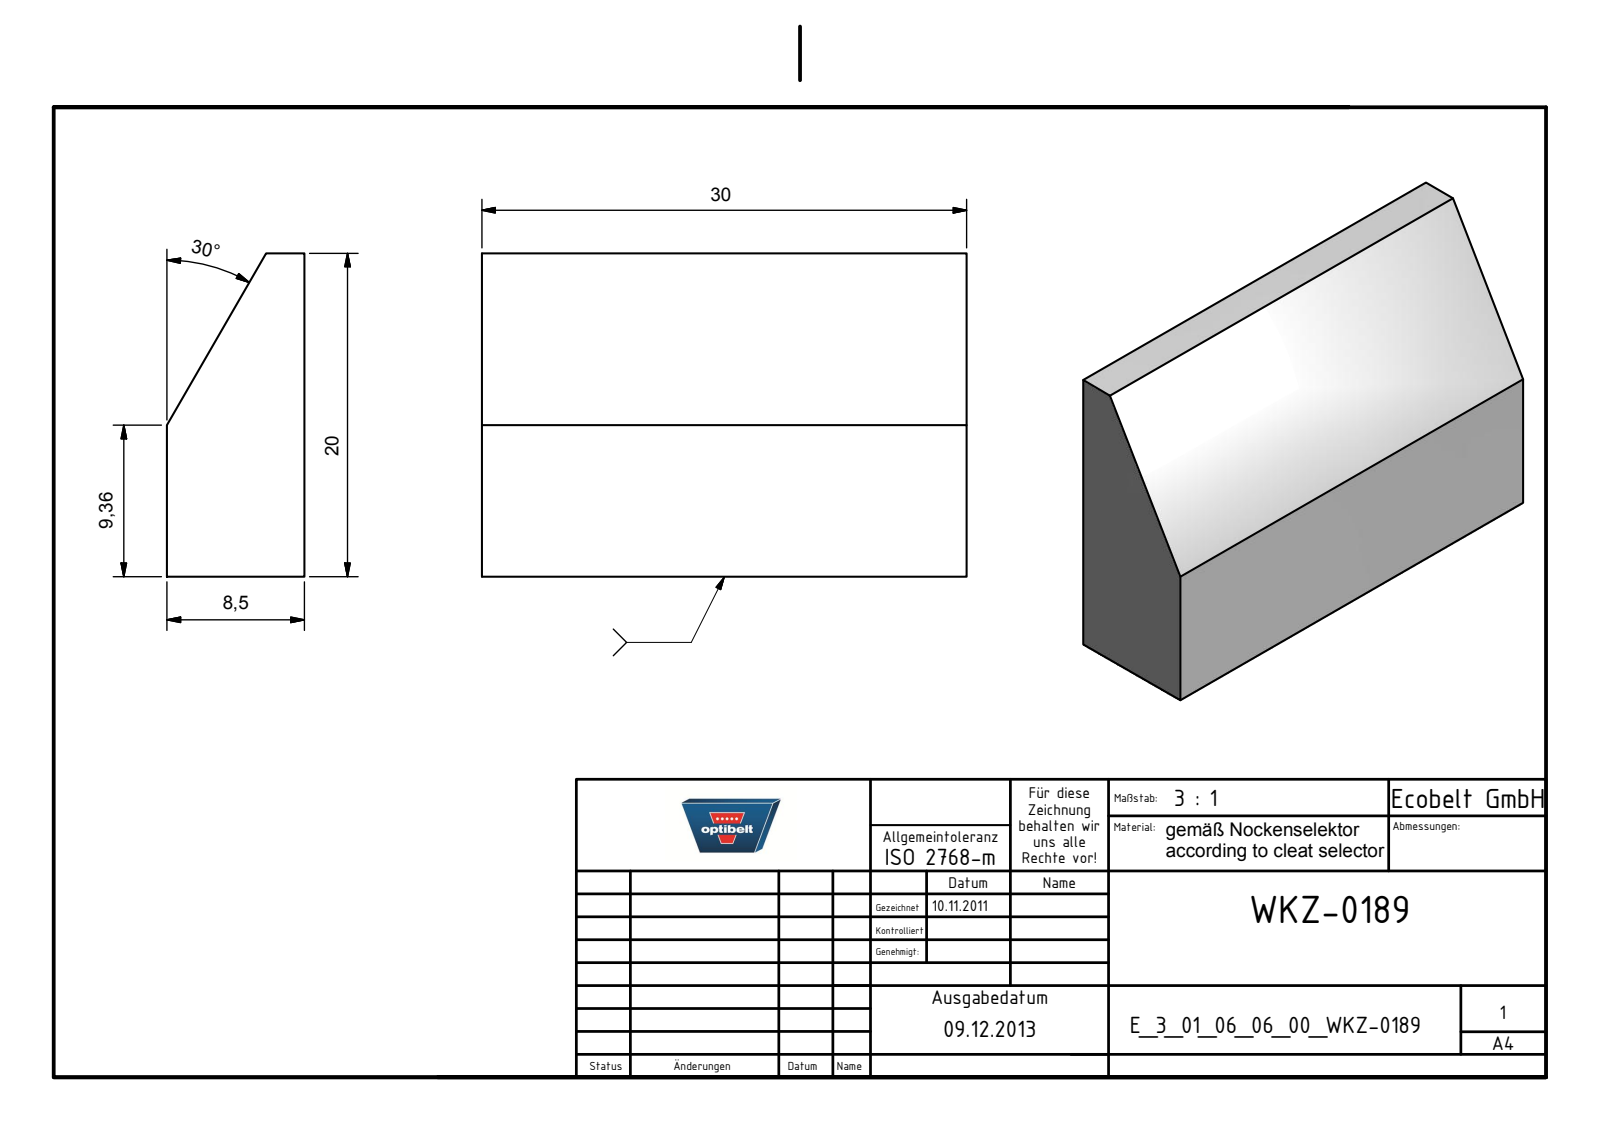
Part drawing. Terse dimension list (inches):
name: E_3_01_06_06_00_WKZ-0189
written by: Autodesk Inventor 2025 (AUTOMOTIVE_DESIGN)
unit: in
bodies: 1 solid, 7 faces (7 planar, 0 cylindrical, 0 other)
size: 1.181 × 0.787 × 0.335
volume: 0.251 in³; area: 2.868 in²
face distances: 0.335, 1.181, 0.787
